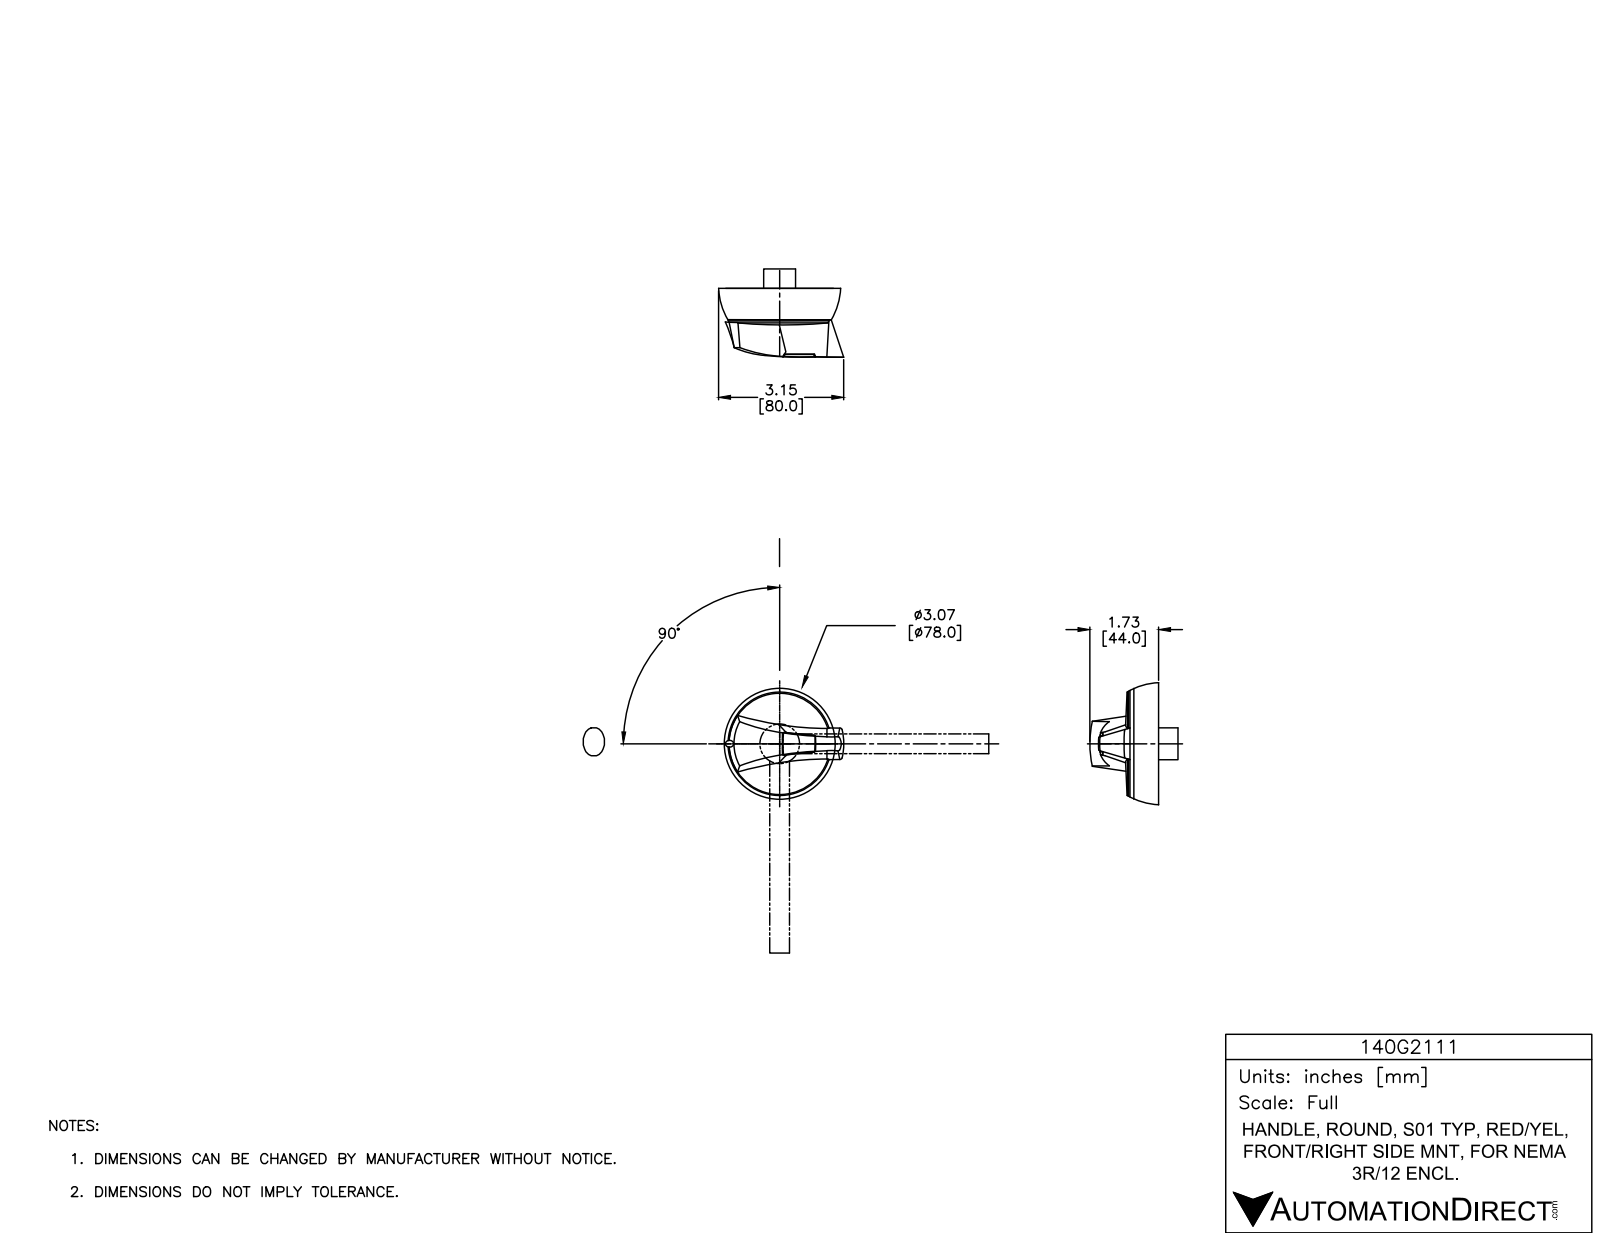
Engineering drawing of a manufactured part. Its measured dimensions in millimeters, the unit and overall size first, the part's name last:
Units: millimetres
Overall size (bounding box): 79.9 × 78 × 51.5
Round holes (diameter × count): ⌀4 ×6, ⌀10.8 ×4, ⌀0.8 ×3, ⌀4.3 ×2, ⌀8.6 ×2, ⌀9.2 ×2, ⌀4.8 ×1, ⌀76 ×1
Round bosses / shafts (diameter × count): ⌀0.5 ×11, ⌀8 ×4, ⌀2.3 ×3, ⌀1.8 ×3, ⌀5.8 ×2, ⌀71.6 ×1, ⌀68.6 ×1, ⌀66.8 ×1
Partial cylindrical surfaces — rounded edges, fillets, slot ends (radius × count): R0.3 ×221, R0.4 ×20, R0.9 ×20, R0.8 ×15, R0.6 ×3, R200 ×2, R0.3 ×1, R2 ×1
Main face-to-face distances: 0.6, 15.8, 39.1, 23.3, 0.9, 15.5, 38.8, 15.2, 38.5, 6.2
Hole centre spacings: 24.4, 7.8, 27.9, 28, 30.6, 40, 47.8, 48.8
Volume: 132 400 mm³ · Surface area: 36 780 mm²
Bodies: 9 solids, 1345 faces (711 planar, 526 cylindrical, 108 other)
Part name (STEP PRODUCT): 140G2111
STEP written by: SolidWorks 2015 (AUTOMOTIVE_DESIGN)
